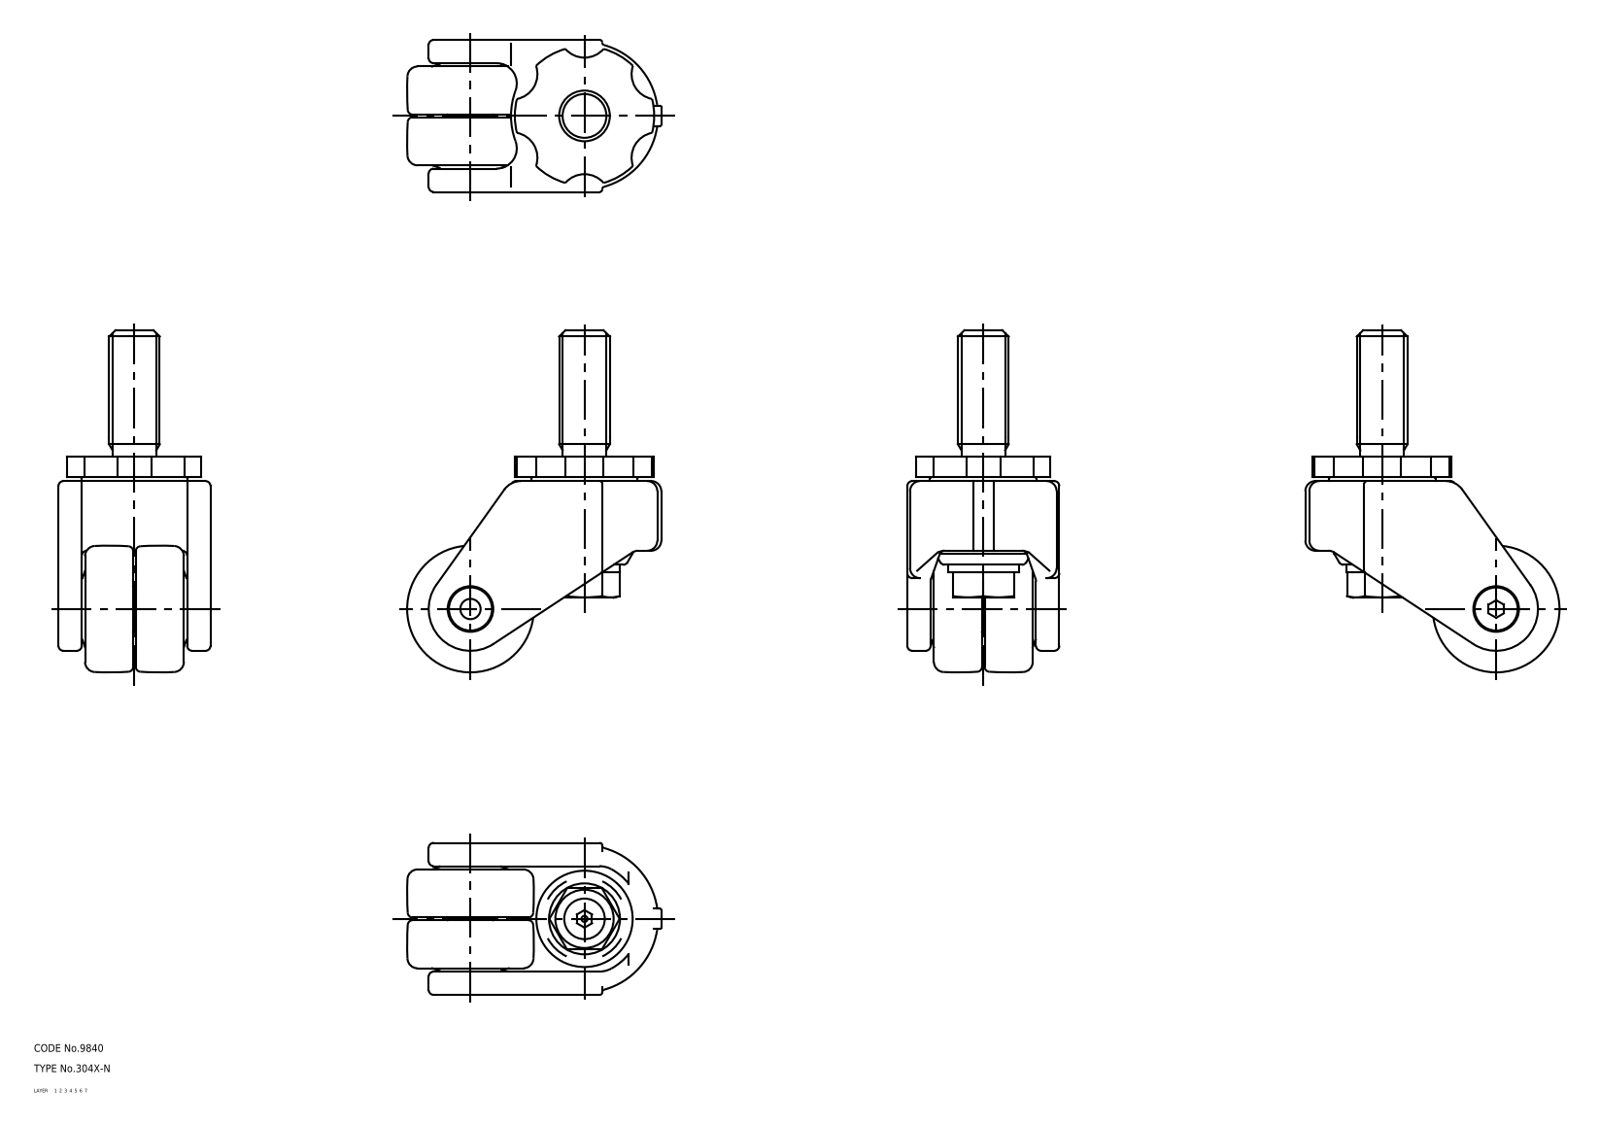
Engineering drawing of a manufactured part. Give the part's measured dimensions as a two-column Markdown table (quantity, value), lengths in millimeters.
| quantity | value |
| --- | --- |
| part name | wheel; main shaft; axle; No_304X_N_23482_36 |
| STEP written by | CADfix (AUTOMOTIVE_DESIGN) |
| units | millimeters |
| bodies | 4 solids, 234 faces (0 planar, 0 cylindrical, 234 other) |
| overall size | 135 × 100.3 × 60 |
| volume | 241 472 mm³ |
| surface area | 53 683 mm² |
